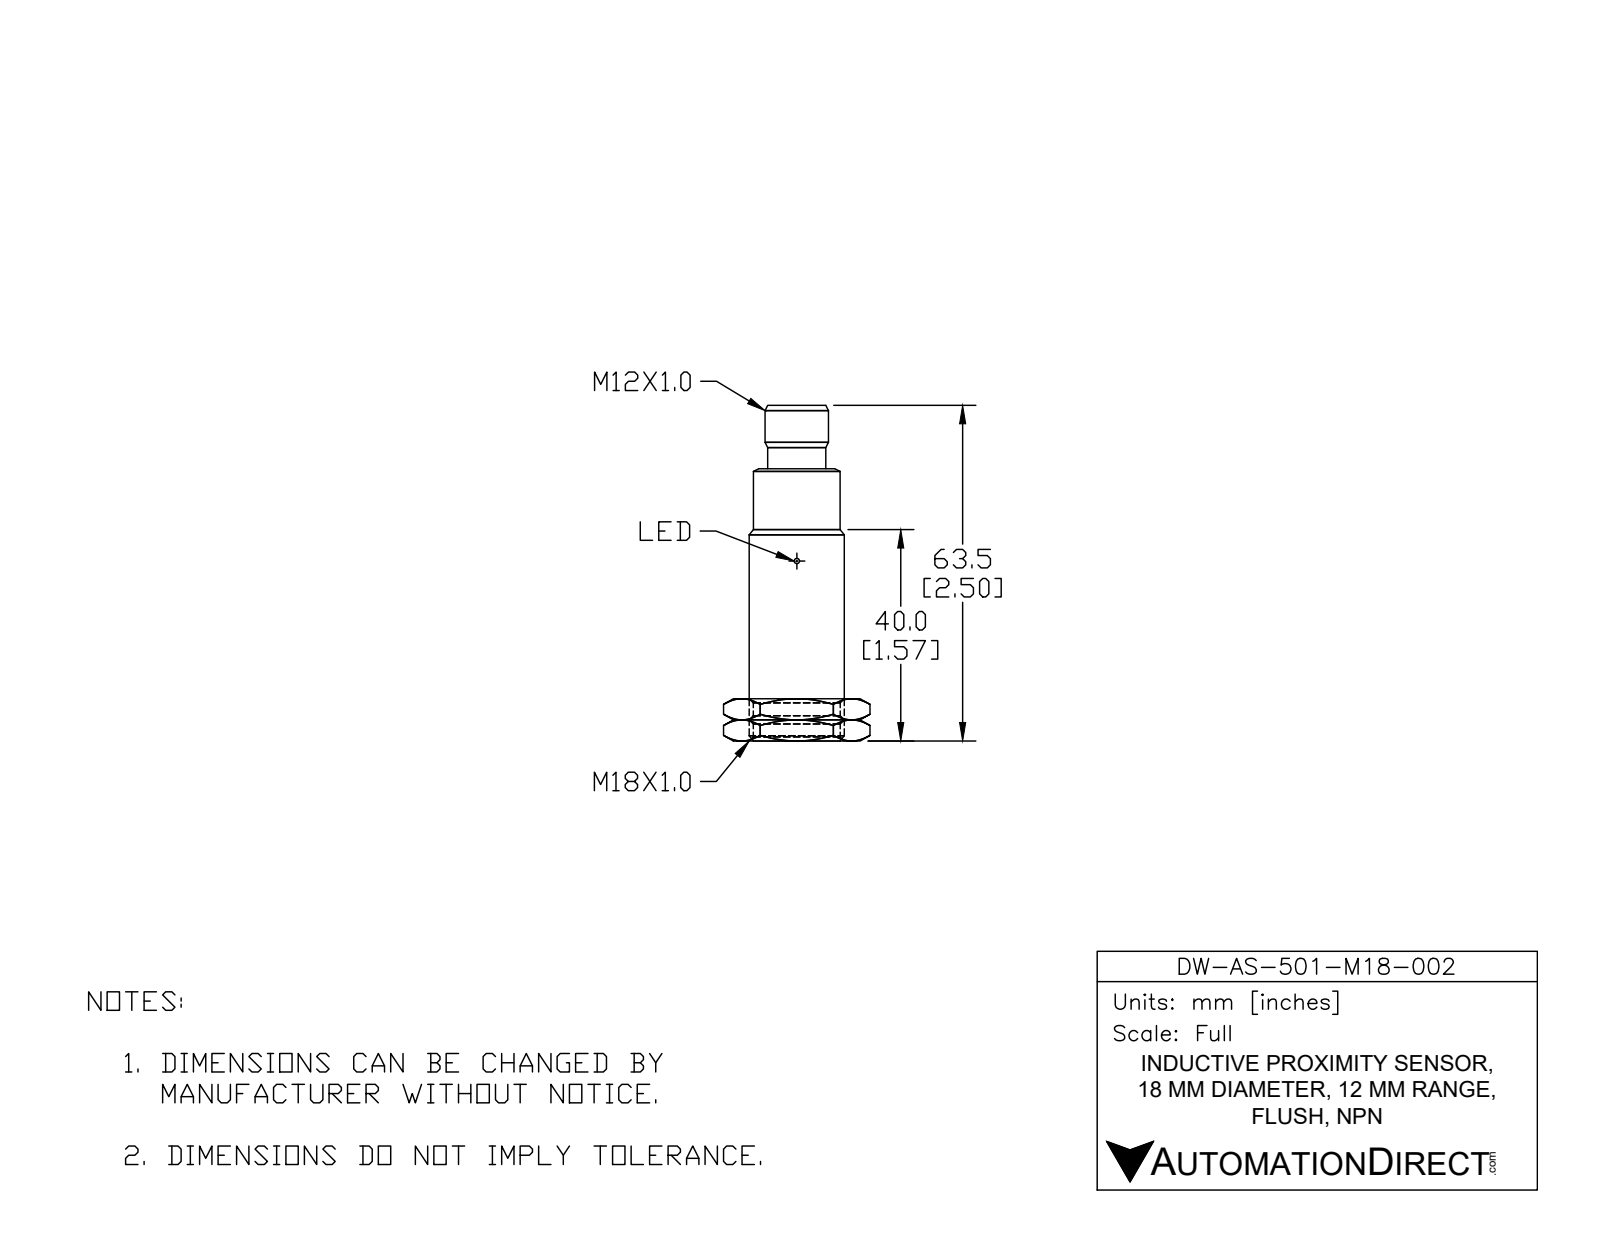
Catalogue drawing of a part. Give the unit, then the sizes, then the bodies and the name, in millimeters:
Units: millimetres
Overall size (bounding box): 63.6 × 18 × 18
Round holes (diameter × count): ⌀3 ×2, ⌀8.5 ×1
Round bosses / shafts (diameter × count): ⌀1 ×4, ⌀18 ×1, ⌀16.4 ×1, ⌀12 ×1, ⌀10.5 ×1
Partial cylindrical surfaces — rounded edges, fillets, slot ends (radius × count): R0.6 ×2, R4.9 ×1
Main face-to-face distances: 50.5, 54.9, 4.4, 63.6, 13.1, 8.7, 1.1, 41.5, 9, 13.4
Volume: 13 300 mm³ · Surface area: 4 126 mm²
Bodies: 1 solid, 38 faces (8 planar, 20 cylindrical, 10 other)
Part name (STEP PRODUCT): DW-AS-501-M18-002
STEP written by: SolidWorks 2017 (AUTOMOTIVE_DESIGN)
